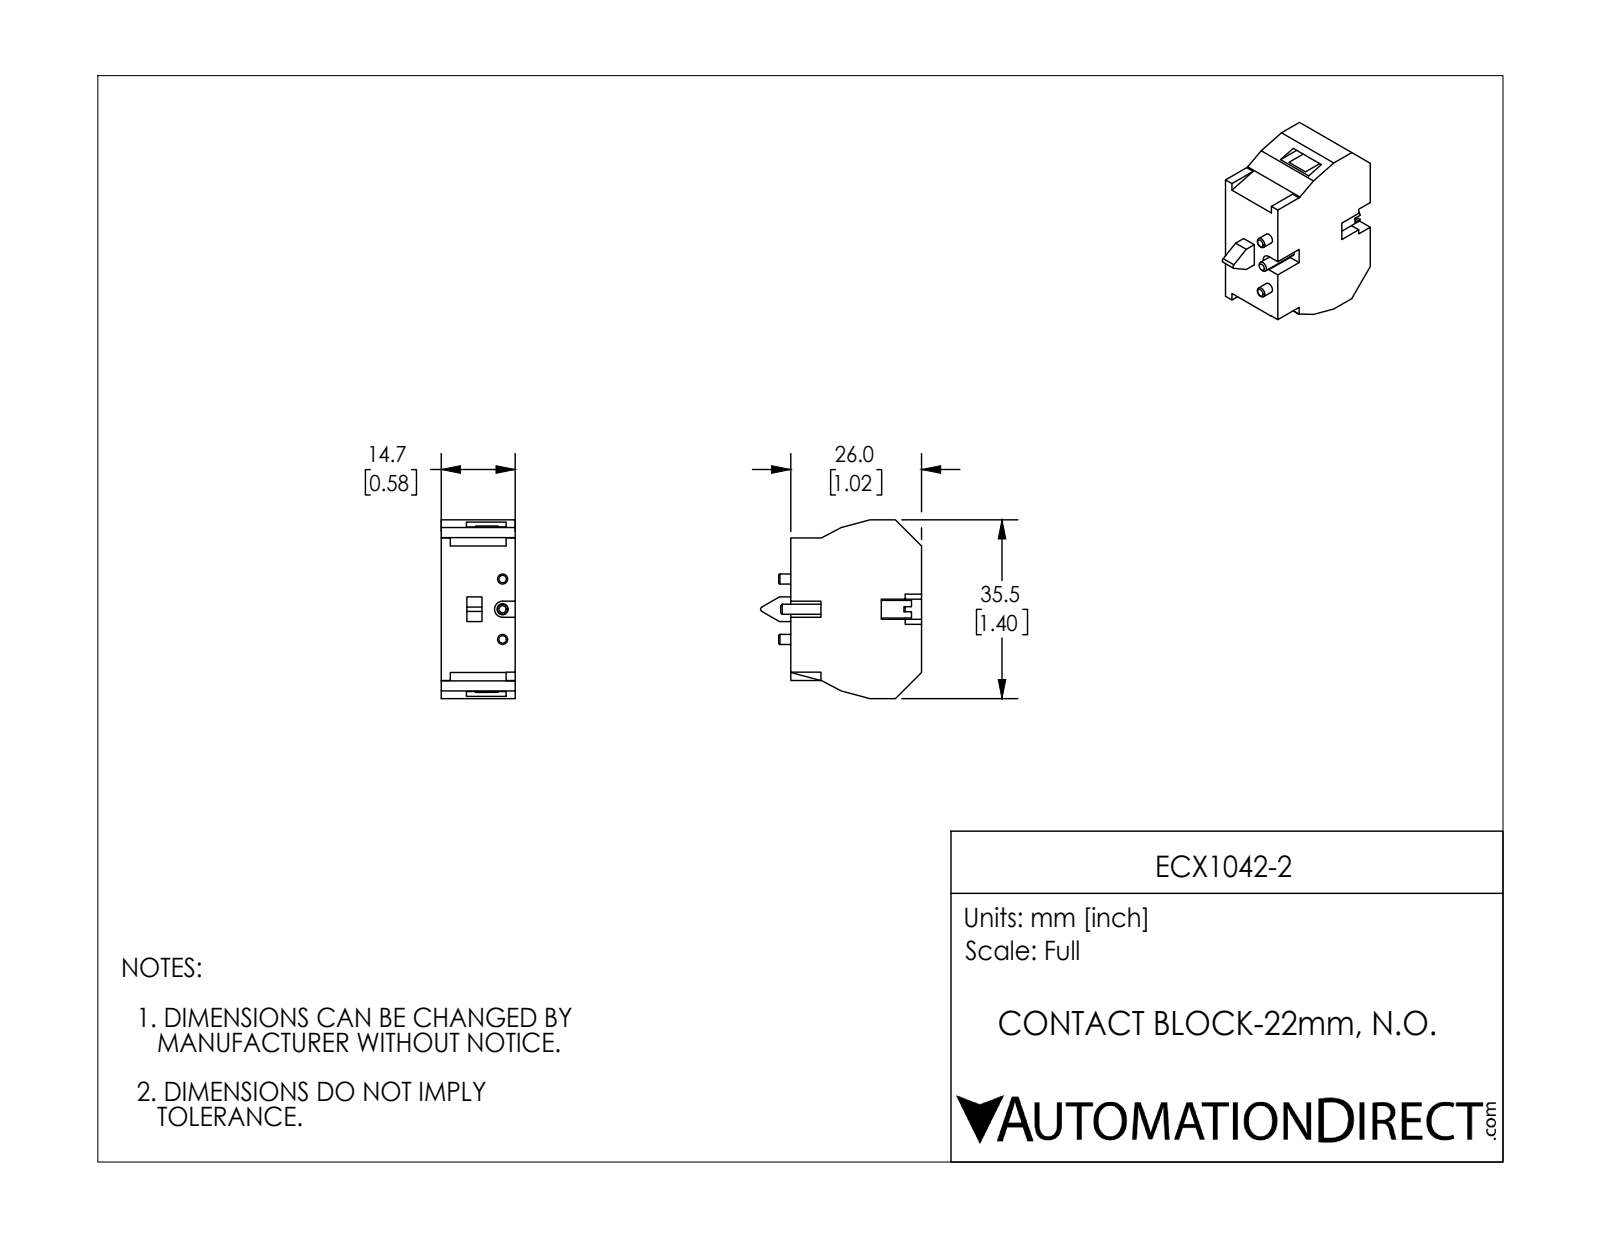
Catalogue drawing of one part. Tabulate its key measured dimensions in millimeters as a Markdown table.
| quantity | value |
| --- | --- |
| part name | ECX1042-2 |
| STEP written by | SolidWorks 2016 (AUTOMOTIVE_DESIGN) |
| units | millimeters |
| bodies | 1 solid, 93 faces (75 planar, 14 cylindrical, 4 other) |
| overall size | 35.54 × 32 × 14.7 |
| volume | 10 661 mm³ |
| surface area | 4 346 mm² |
| round holes (diameter × count) | 2 × 2, 2.2 × 1 |
| partial cylindrical surfaces (radius × count) | 0.5 × 1, 1.6 × 1, 2 × 1 |
| main face-to-face distances | 14.7, 26, 6.84, 7.86, 0.45, 12.9, 6.87, 28.67, 0.95, 35.09 |
| hole center spacings | 6, 12 |
